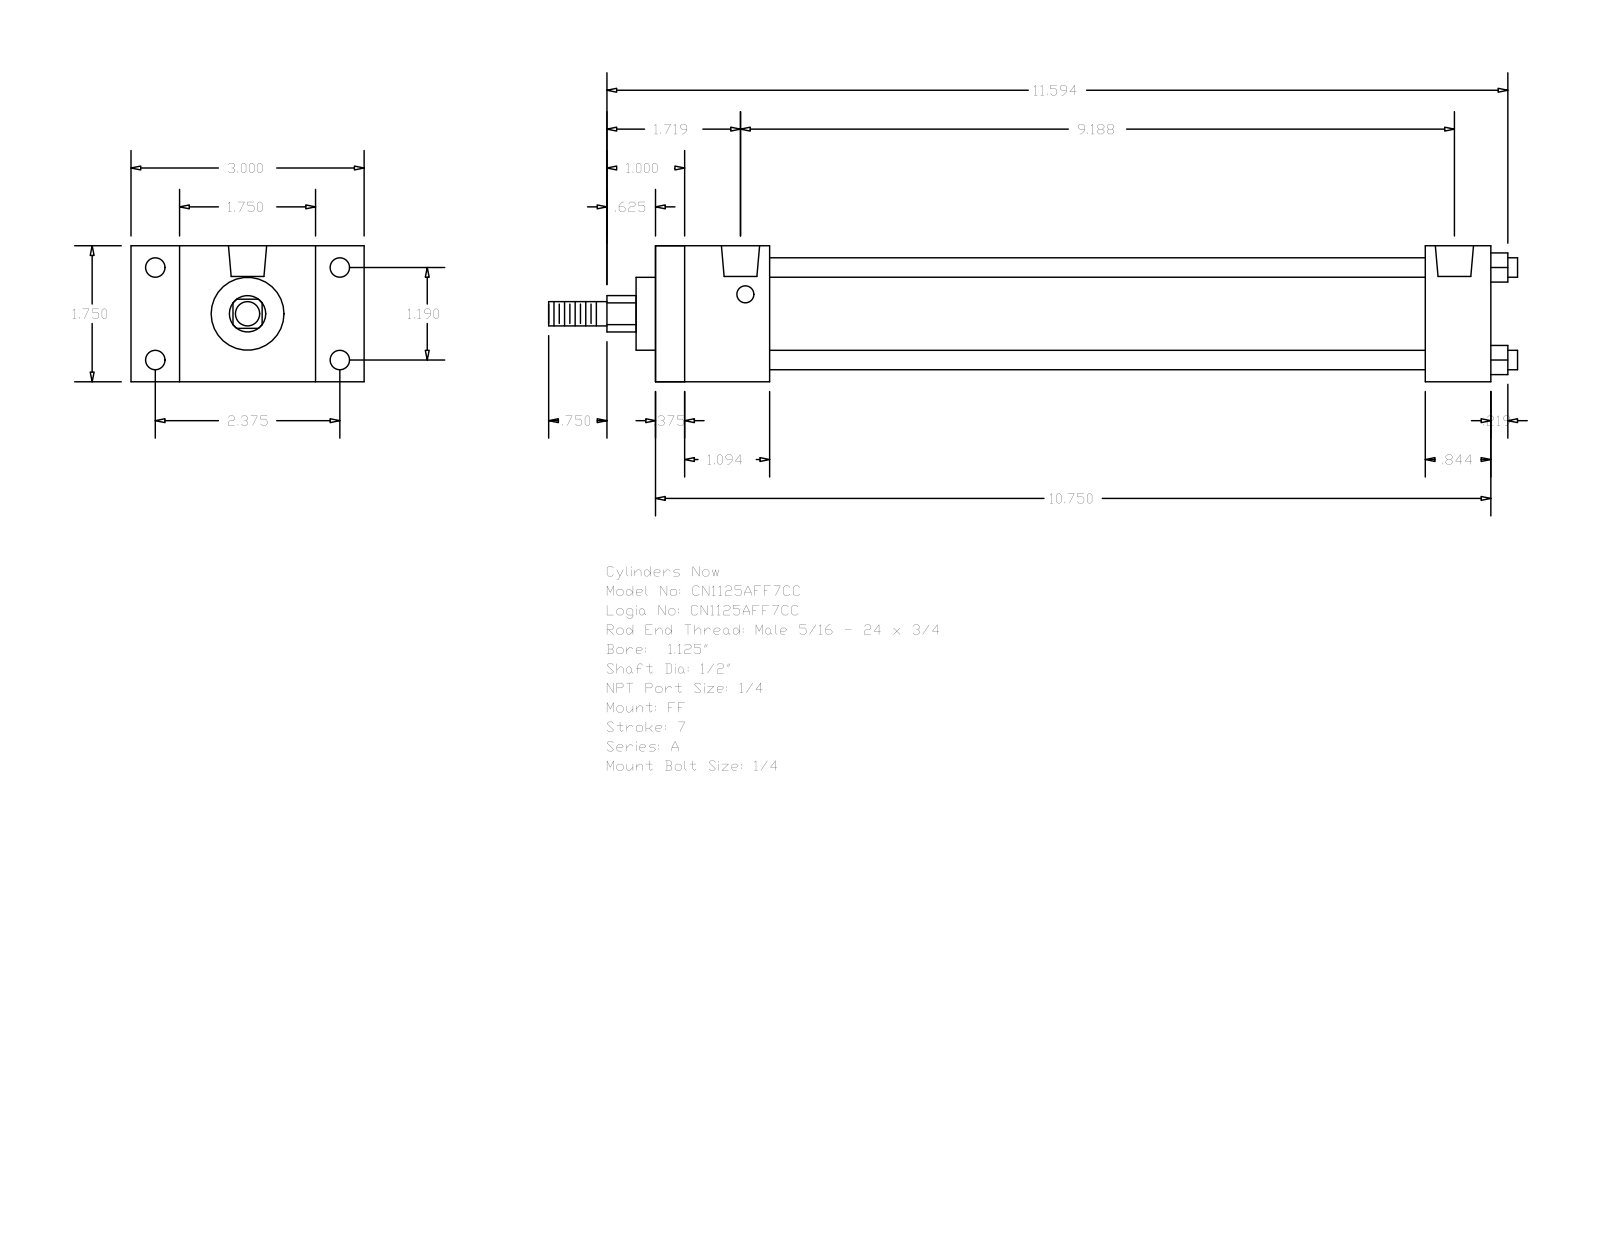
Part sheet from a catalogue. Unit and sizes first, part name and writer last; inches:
Units: inches
Overall size (bounding box): 12.469 × 3 × 1.75
Round holes (diameter × count): ⌀0.219 ×4, ⌀0.25 ×4, ⌀0.492 ×2
Round bosses / shafts (diameter × count): ⌀0.25 ×4, ⌀1.255 ×1, ⌀0.937 ×1, ⌀0.5 ×1, ⌀0.313 ×1
Partial cylindrical surfaces — rounded edges, fillets, slot ends (radius × count): R0.234 ×1
Main face-to-face distances: 1.75, 10.75, 0.375, 10.375, 0.625, 9.906, 9.531, 0.844, 1.469, 1.094
Hole centre spacings: 1.19, 2.375, 2.656, 9.063, 0.062, 0.063, 9.125, 9.125
Bodies: 0 solids, 92 faces (64 planar, 28 cylindrical, 0 other)
Part name (STEP PRODUCT): A_FF__0112_0.5
STEP written by: GSSL Pune (CONFIG_CONTROL_DESIGN)
